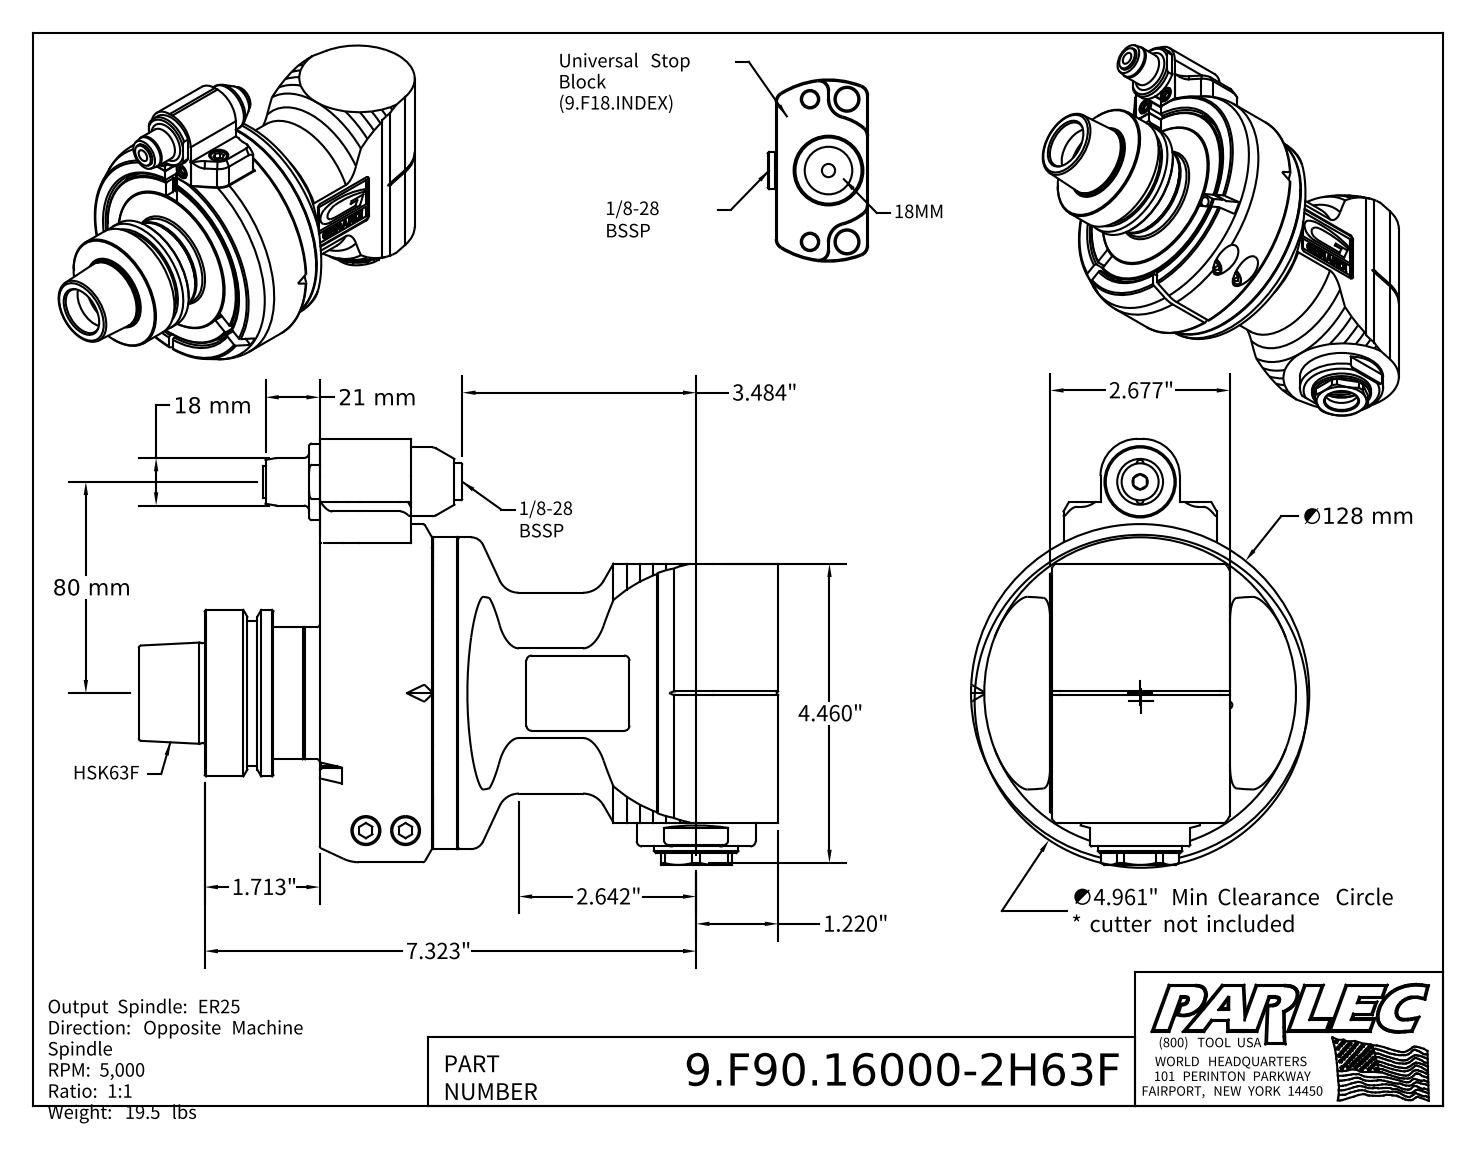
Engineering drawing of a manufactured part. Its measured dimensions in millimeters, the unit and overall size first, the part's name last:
Units: millimetres
Overall size (bounding box): 242 × 161.25 × 128
Round holes (diameter × count): ⌀4.2 ×4, ⌀5 ×4, ⌀2.6 ×2, ⌀5.3 ×2, ⌀8 ×2, ⌀10.4 ×2, ⌀11 ×2, ⌀12.5 ×2, ⌀2.5 ×1, ⌀3 ×1, ⌀3.3 ×1, ⌀6.5 ×1
Round bosses / shafts (diameter × count): ⌀10 ×4, ⌀6 ×4, ⌀2.5 ×2, ⌀128 ×1, ⌀118 ×1, ⌀99 ×1, ⌀63 ×1, ⌀55 ×1
Partial cylindrical surfaces — rounded edges, fillets, slot ends (radius × count): R2 ×12, R4 ×4, R0.4 ×2, R0.5 ×2, R1 ×2, R8 ×2, R14 ×2, R11 ×1
Main face-to-face distances: 0.5, 7, 35, 35.5, 34, 7.5, 42.5, 8, 8.5, 26
Hole centre spacings: 7, 13, 19.01, 25.54, 63.26, 1.2, 14, 15
Volume: 1 469 000 mm³ · Surface area: 180 497 mm²
Bodies: 8 solids, 908 faces (598 planar, 127 cylindrical, 183 other)
Part name (STEP PRODUCT): F90_16_HSK_F63; F90-16; ANTI_50_HSK_F63; VSTCE_ISO4027_M5x10.1 (+6 more)
STEP written by: Autodesk Inventor 2020 (AUTOMOTIVE_DESIGN)
